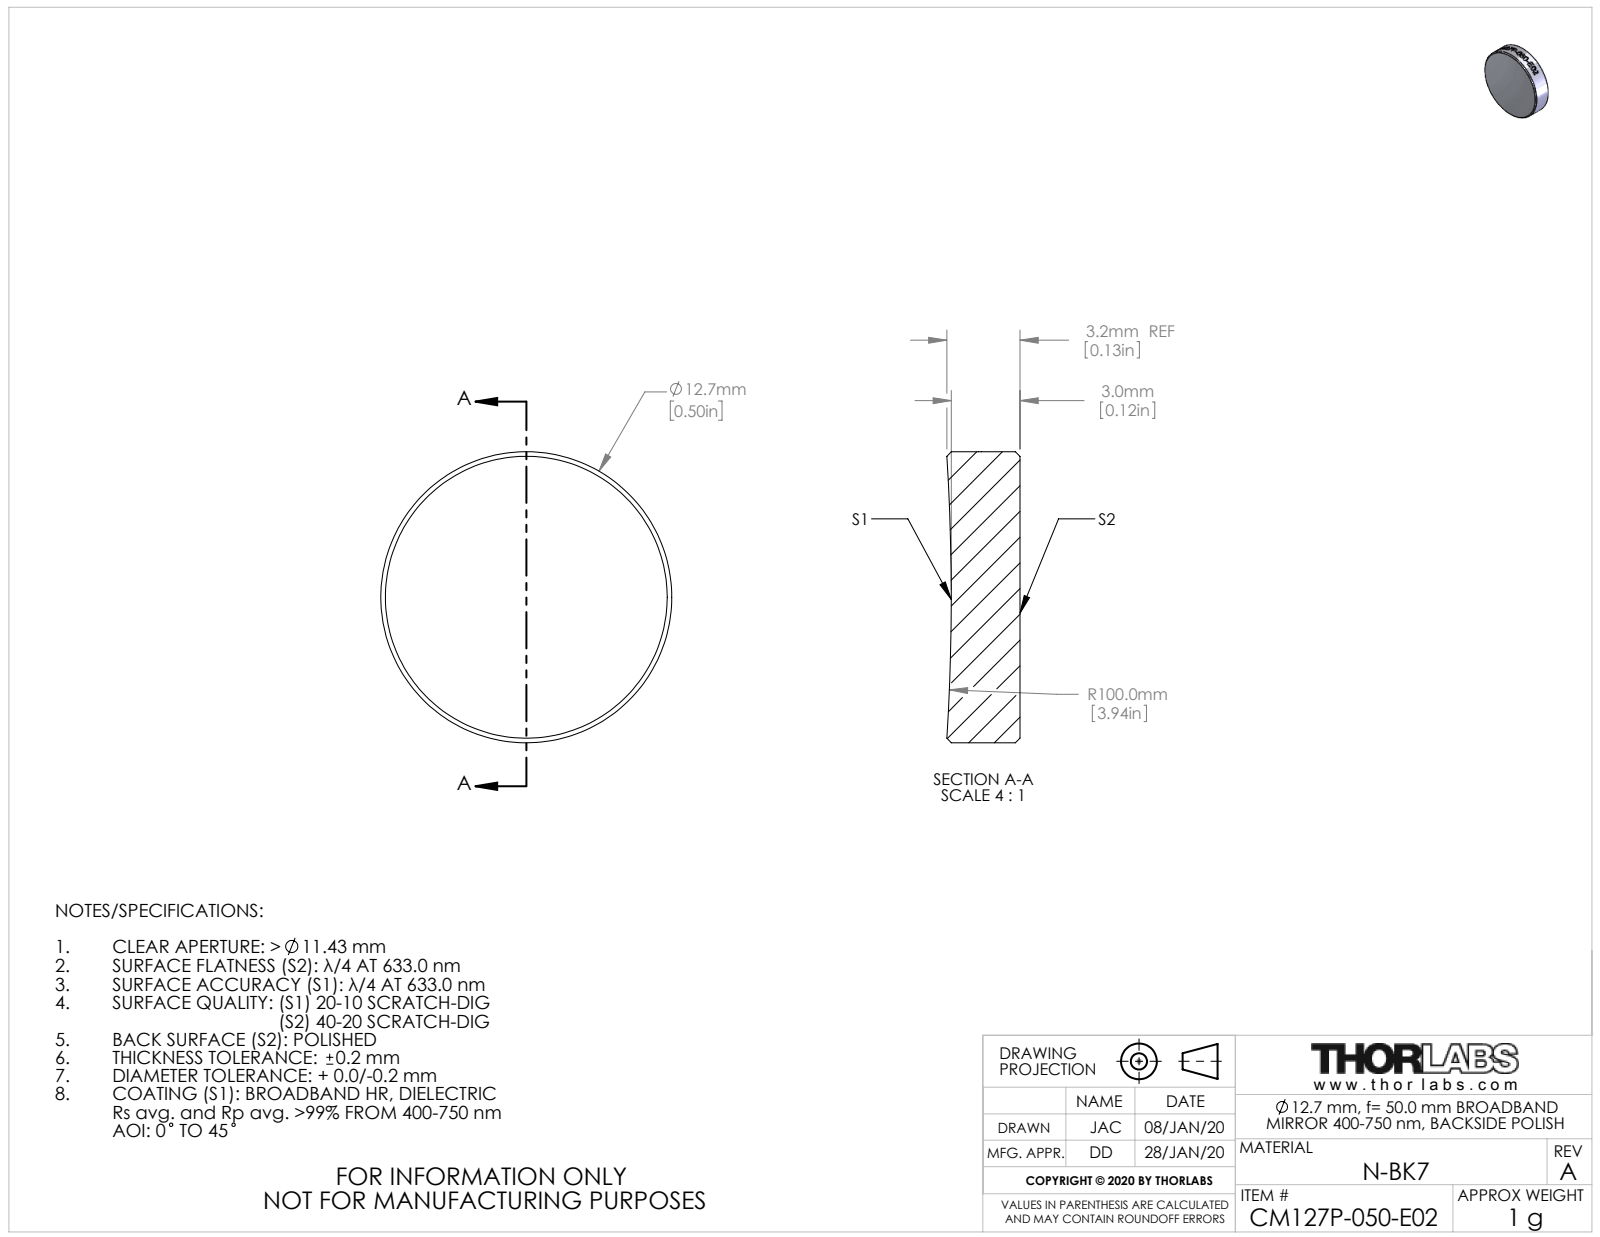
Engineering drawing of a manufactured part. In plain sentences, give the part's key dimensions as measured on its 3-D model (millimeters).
The part is named "TTN201208-E0W". Its 3-D file was written by "SolidWorks 2018 (CONFIG_CONTROL_DESIGN)". It is 1 solid with 27 faces: 1 planar, 20 cylindrical and 6 other. Overall it measures 12.7 by 12.7 by 3.19 millimeters. Its volume is 391 cubic millimeters and its surface area 371 square millimeters. Round bosses or shafts: 1 of diameter 12.7.
